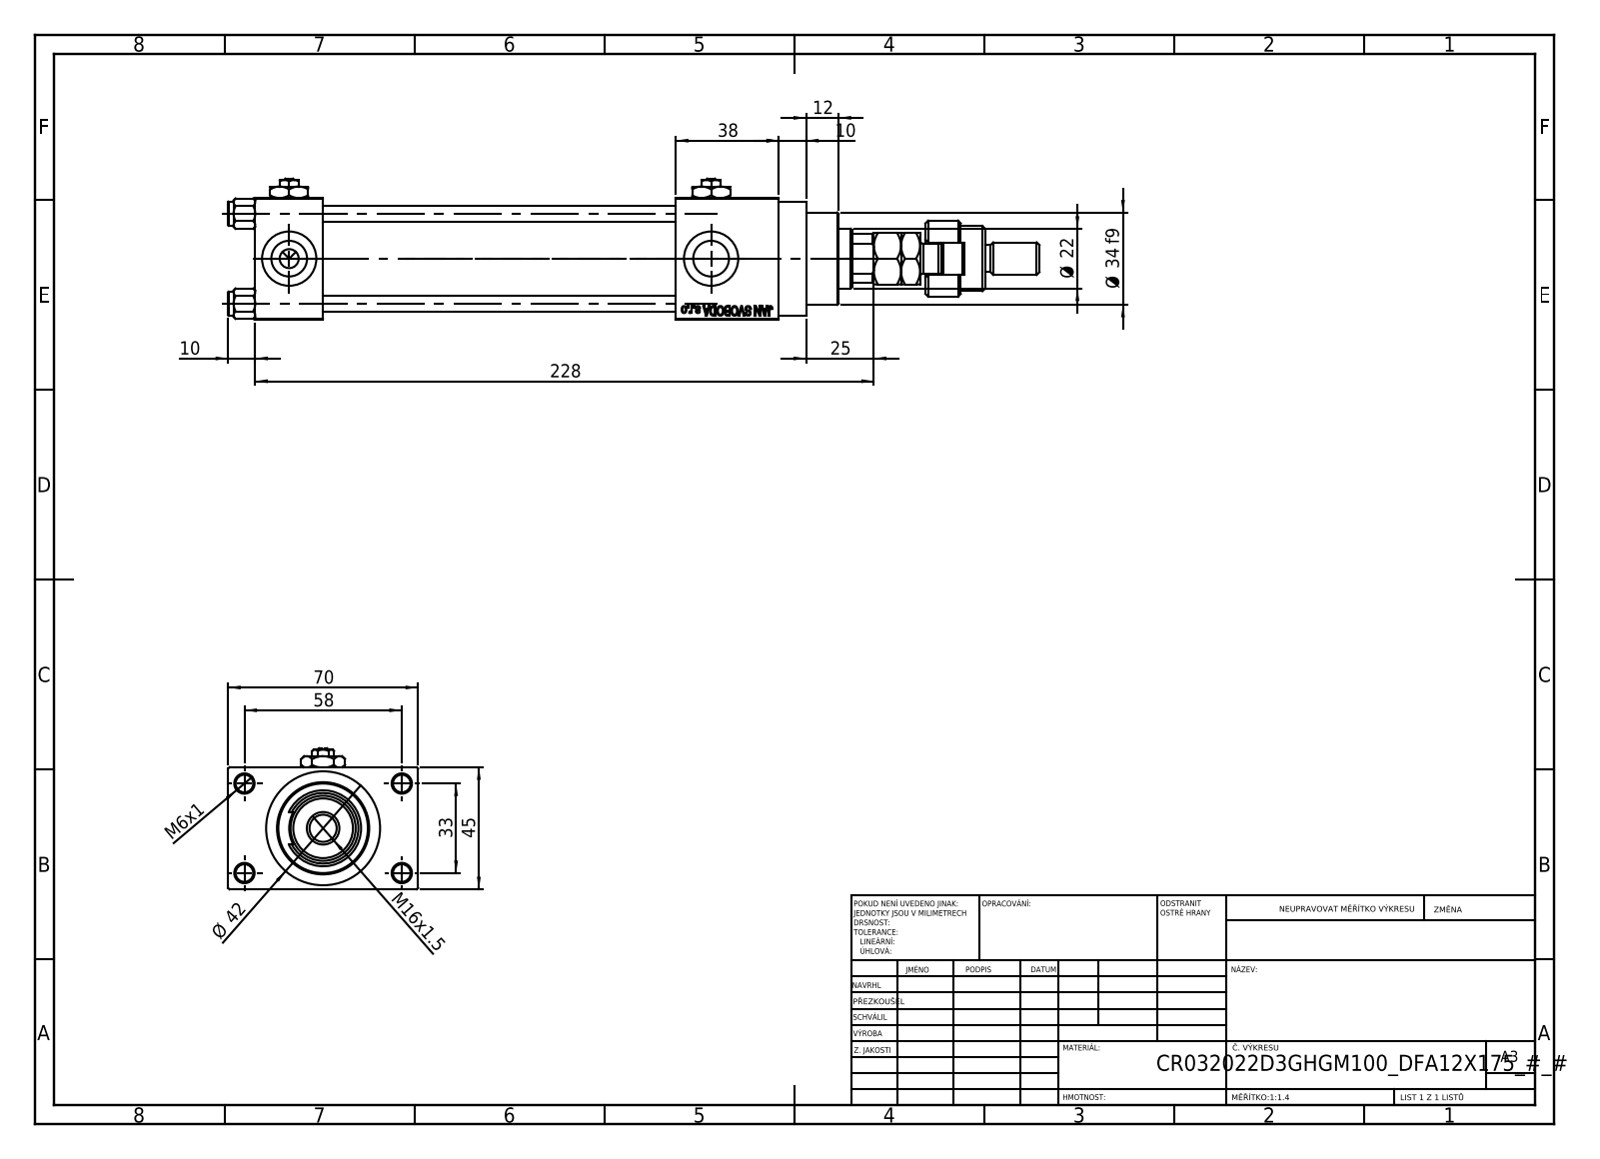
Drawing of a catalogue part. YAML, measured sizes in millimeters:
part_name: "V215CR_VCP_D; MFA; Zatka_pro_OIL_PORT; V215CR_D_TYCINKA (+4 more)"
step_written_by: "SolidWorks 2019 (CONFIG_CONTROL_DESIGN)"
units: millimeters
bodies: {solids: 15, faces: 1286, planar: 570, cylindrical: 112, other: 604}
overall_size: [299, 70, 52]
volume: 325473
surface_area: 117988
round_holes:
  - {diameter: 6, count: 4}
  - {diameter: 6.5, count: 4}
  - {diameter: 13.16, count: 4}
  - {diameter: 20, count: 4}
  - {diameter: 7, count: 3}
  - {diameter: 10.5, count: 1}
  - {diameter: 22, count: 1}
  - {diameter: 24, count: 1}
  - {diameter: 25, count: 1}
  - {diameter: 32, count: 1}
  - {diameter: 33, count: 1}
round_bosses_or_shafts:
  - {diameter: 9, count: 4}
  - {diameter: 42, count: 1}
  - {diameter: 38, count: 1}
  - {diameter: 34, count: 1}
  - {diameter: 28, count: 1}
  - {diameter: 18, count: 1}
  - {diameter: 12, count: 1}
  - {diameter: 11, count: 1}
partial_cylinders:
  - {radius: 9.75, count: 1}
  - {radius: 10.5, count: 1}
face_to_face_distances: [45, 25, 12.5, 130, 155, 57.5, 38, 168, 193, 70]
hole_center_spacings: [12.4, 23.48, 33.2, 33.37, 35.35, 45.6, 56.35, 33]
